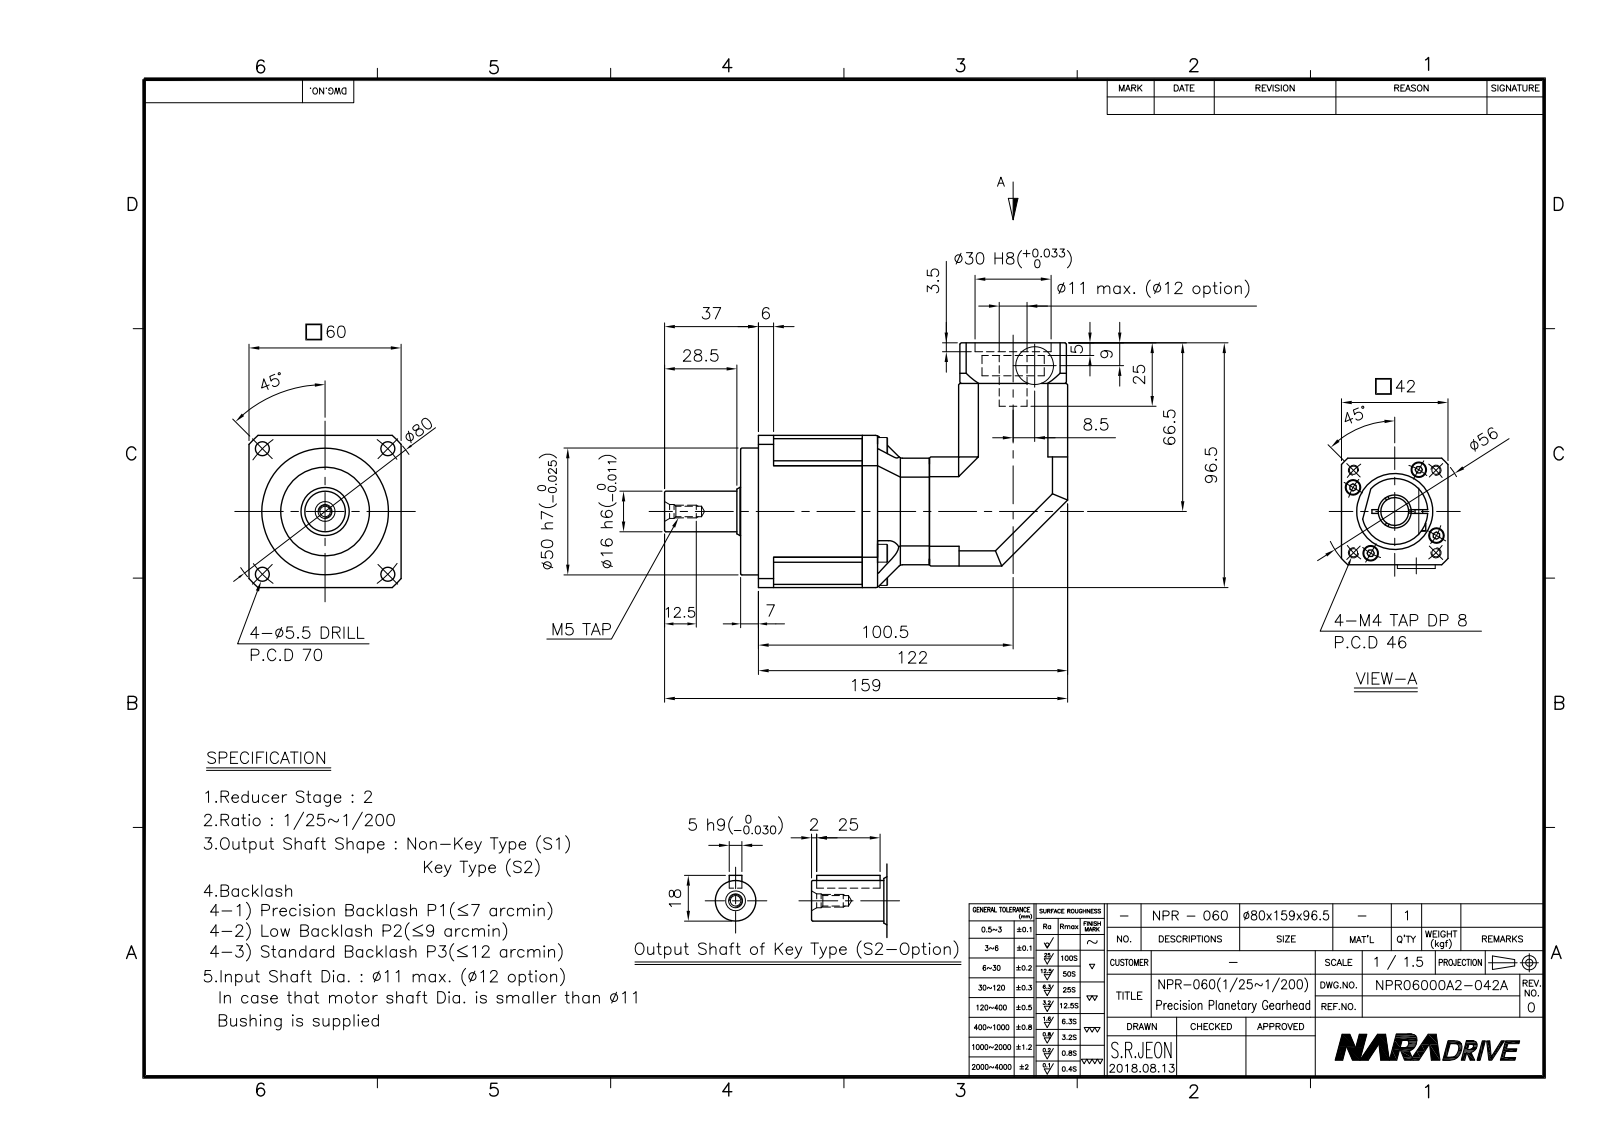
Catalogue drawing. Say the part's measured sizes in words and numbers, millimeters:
The part is named "NPR06000A2-042A-S1". Its 3-D file was written by "Autodesk Inventor 2015 (AUTOMOTIVE_DESIGN)". It is 2 solids with 516 faces: 252 planar, 132 cylindrical and 132 other. Overall it measures 159 by 96.5 by 60 millimeters. Its volume is 336 628 cubic millimeters and its surface area 59 536 square millimeters. Round holes: 9 of diameter 2.46, 9 of diameter 3.4, 8 of diameter 3.24, 8 of diameter 6, 4 of diameter 4.2, 4 of diameter 5.5, 1 of diameter 4.13, 1 of diameter 7, 1 of diameter 8.5, 1 of diameter 11, 1 of diameter 13, 1 of diameter 28. Round bosses or shafts: 9 of diameter 5.5, 9 of diameter 3, 4 of diameter 7, 4 of diameter 4, 1 of diameter 50, 1 of diameter 35, 1 of diameter 26, 1 of diameter 19. Partial cylindrical surfaces (rounded edges, fillets, slot ends): 8 of radius 2, 8 of radius 7, 2 of radius 25.5, 1 of radius 3, 1 of radius 28, 1 of radius 35, 1 of radius 40. The main face-to-face distances are 8.5, 51.5, 51, 60, 43, 0.5, 42.5, 5, 9, 7.5. The hole center spacings are 15.5, 20.75, 36.68, 19, 32.53, 33.41, 51, 51.15.
